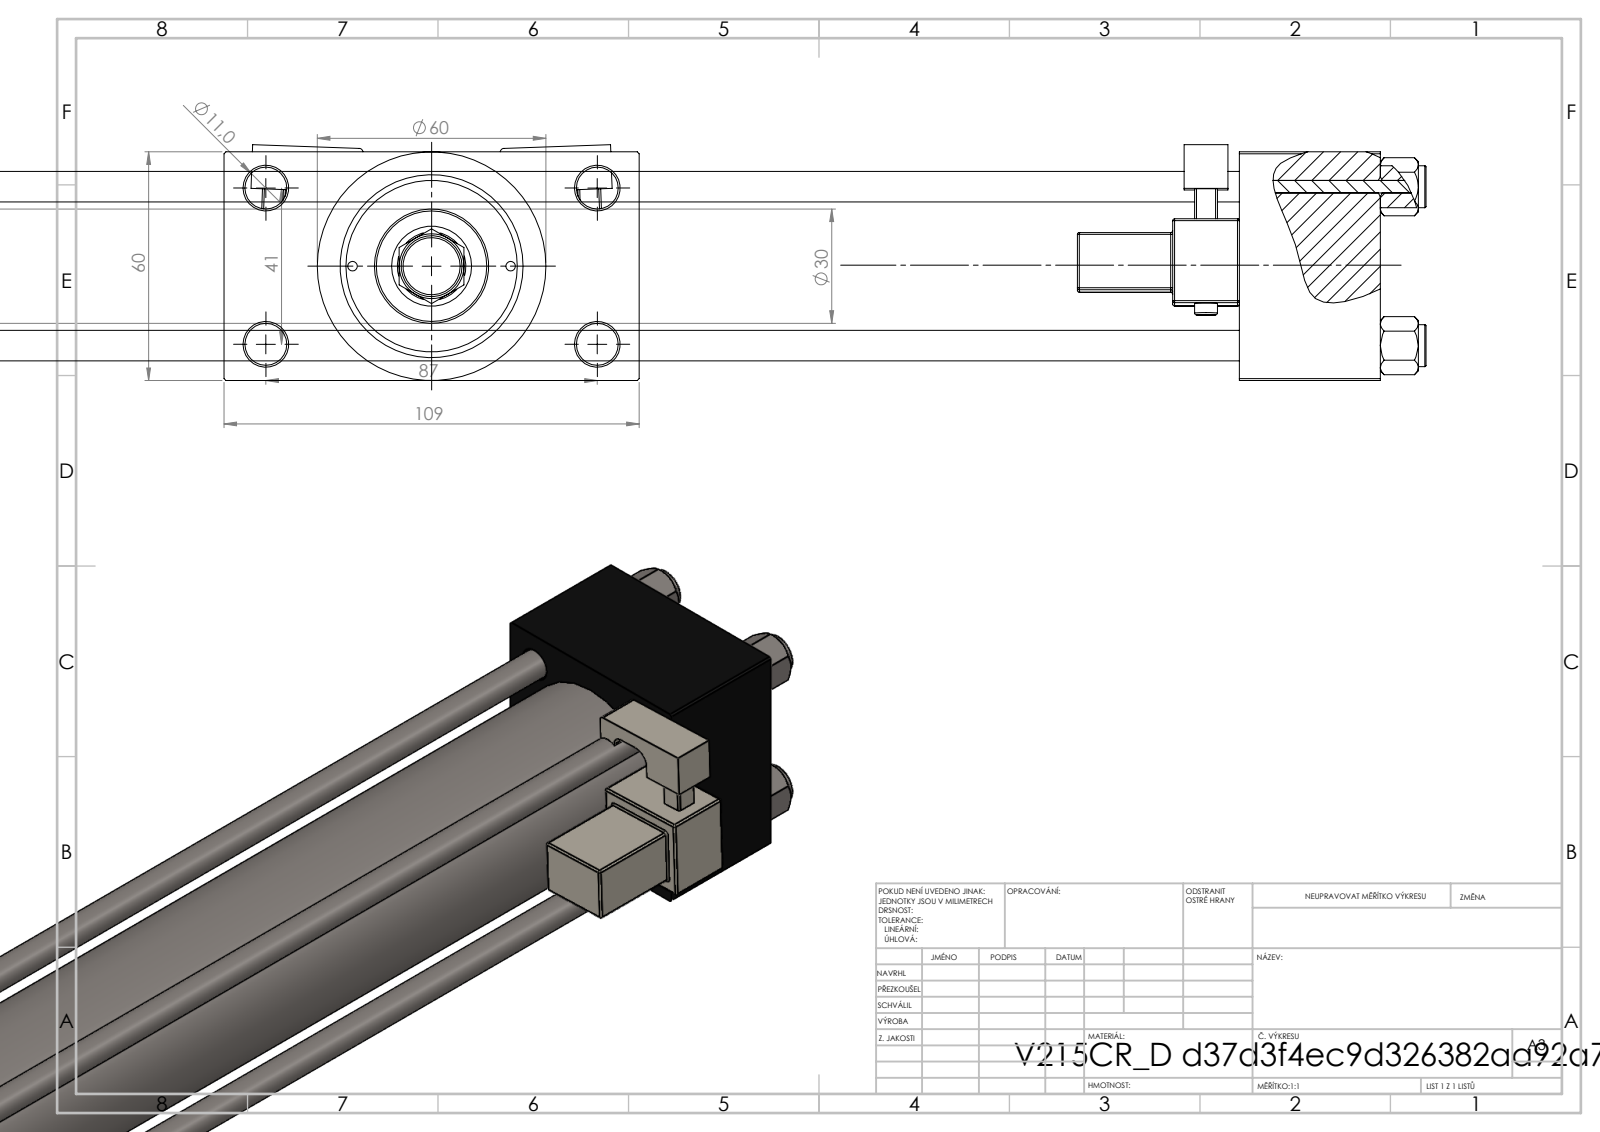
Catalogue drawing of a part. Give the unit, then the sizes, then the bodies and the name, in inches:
Units: inches
Overall size (bounding box): 23.346 × 4.291 × 2.437
Round holes (diameter × count): ⌀0.315 ×4, ⌀0.433 ×4, ⌀0.098 ×2, ⌀0.276 ×2, ⌀0.656 ×2, ⌀0.945 ×2, ⌀0.335 ×1, ⌀0.709 ×1, ⌀0.827 ×1, ⌀1.22 ×1, ⌀1.575 ×1, ⌀1.772 ×1
Round bosses / shafts (diameter × count): ⌀0.433 ×4, ⌀0.236 ×2, ⌀2.362 ×1, ⌀1.811 ×1, ⌀1.181 ×1, ⌀0.63 ×1, ⌀0.394 ×1
Partial cylindrical surfaces — rounded edges, fillets, slot ends (radius × count): R0.02 ×48, R0.039 ×2, R0.098 ×2, R0.157 ×2, R0.335 ×1
Main face-to-face distances: 2.362, 17.244, 0.965, 3.327, 1.457, 18.701, 20.394, 18.937, 1.693, 4.291
Hole centre spacings: 0.821, 0.892, 1.161, 1.206, 1.642, 1.832, 1.856, 1.893
Volume: 54.05 in³ · Surface area: 463.5 in²
Bodies: 14 solids, 1318 faces (574 planar, 156 cylindrical, 588 other)
Part name (STEP PRODUCT): V215CR_VCP_D; MFA; V215CR_D_Body; V215CR_MSU (+3 more)
STEP written by: SolidWorks 2019 (CONFIG_CONTROL_DESIGN)
